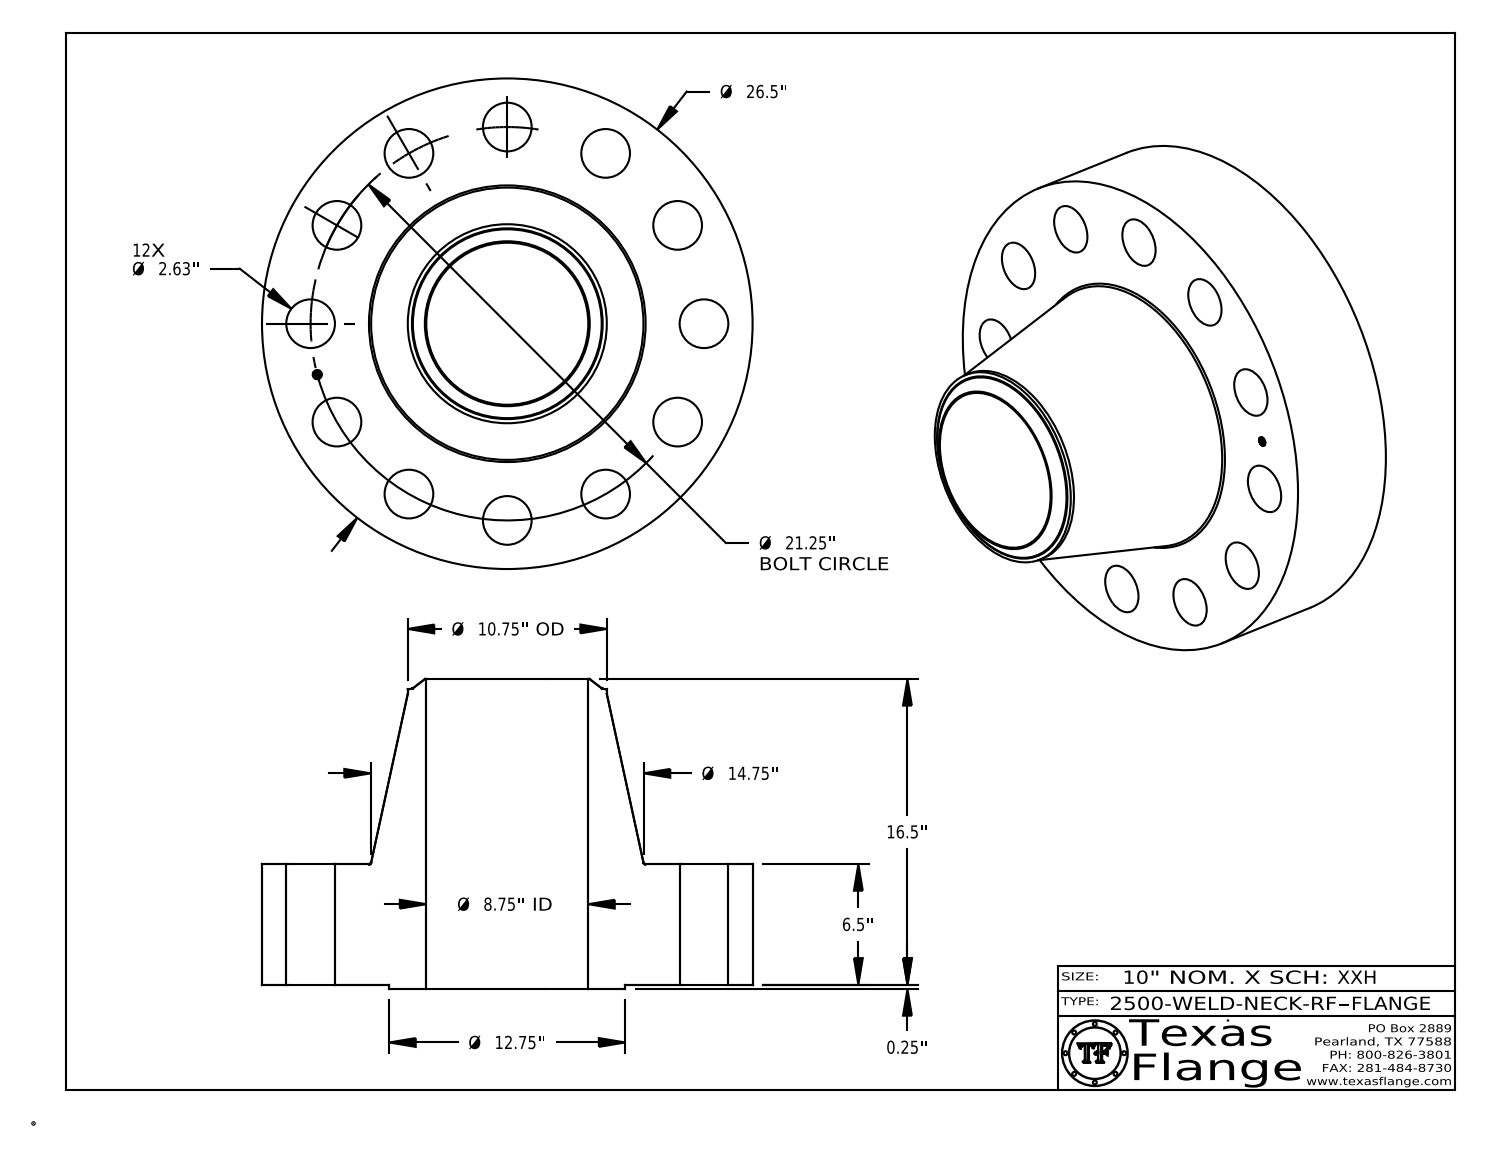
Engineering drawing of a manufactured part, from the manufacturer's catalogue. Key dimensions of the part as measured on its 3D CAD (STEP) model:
Part name (STEP PRODUCT): 2500-WELD-NECK-RF
STEP written by: CATIA V5 STEP AP214 (AUTOMOTIVE_DESIGN)
Units: inches
Bodies: 1 solid, 431 faces (369 planar, 52 cylindrical, 10 other)
Overall size (bounding box): 26.5 × 26.5 × 16.75
Volume: 3 433 in³ · Surface area: 2 818 in²
Round holes (diameter × count): ⌀2.63 ×12, ⌀0.495 ×1, ⌀8.75 ×1
Round bosses / shafts (diameter × count): ⌀0.03 ×8, ⌀26.5 ×1, ⌀12.75 ×1, ⌀10.75 ×1, ⌀0.39 ×1
Main face-to-face distances: 6.5, 0.25, 6.75, 16.75, 16.5, 10, 6.735, 6.485, 0.015, 10.015
Hole centre spacings: 10.625, 5.5, 18.403, 15.026, 20.526, 15.026, 20.526, 21.25
